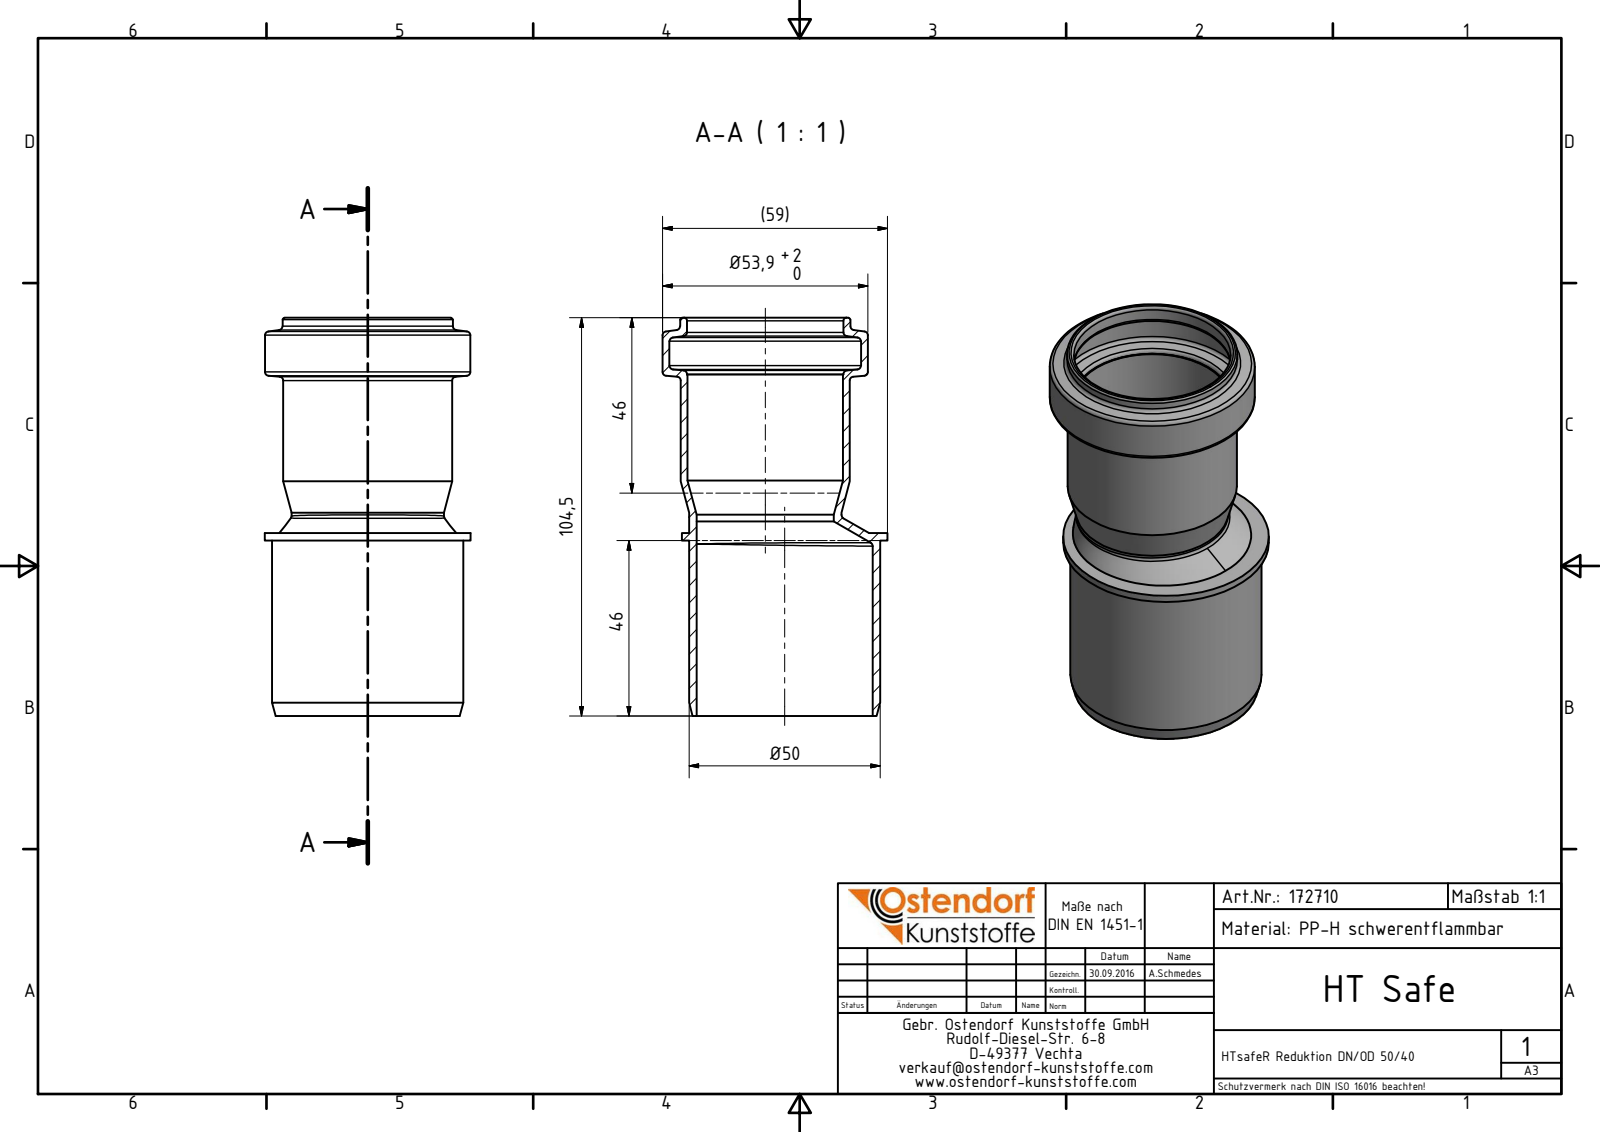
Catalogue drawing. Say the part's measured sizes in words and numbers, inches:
The part is named "172710 HTsafeR DN_OD 50_40". Its 3-D file was written by "Autodesk Inventor 2016 (AUTOMOTIVE_DESIGN)". It is 1 solid with 38 faces: 5 planar, 12 cylindrical and 21 other. Overall it measures 4.114 by 2.325 by 2.126 inches. Its volume is 1.965 cubic inches and its surface area 52.7 square inches. Round holes: 1 of diameter 1.417, 1 of diameter 1.606, 1 of diameter 1.618, 1 of diameter 1.819, 1 of diameter 1.98. Round bosses or shafts: 1 of diameter 2.126, 1 of diameter 2.122, 1 of diameter 1.976, 1 of diameter 1.76, 1 of diameter 1.748, 1 of diameter 1.575. The main face-to-face distances are 0.079, 1.811, 1.89, 4.114, 2.303, 2.224, 3.528, 1.717, 1.638, 0.587. The hole center spacings are 0.201.
